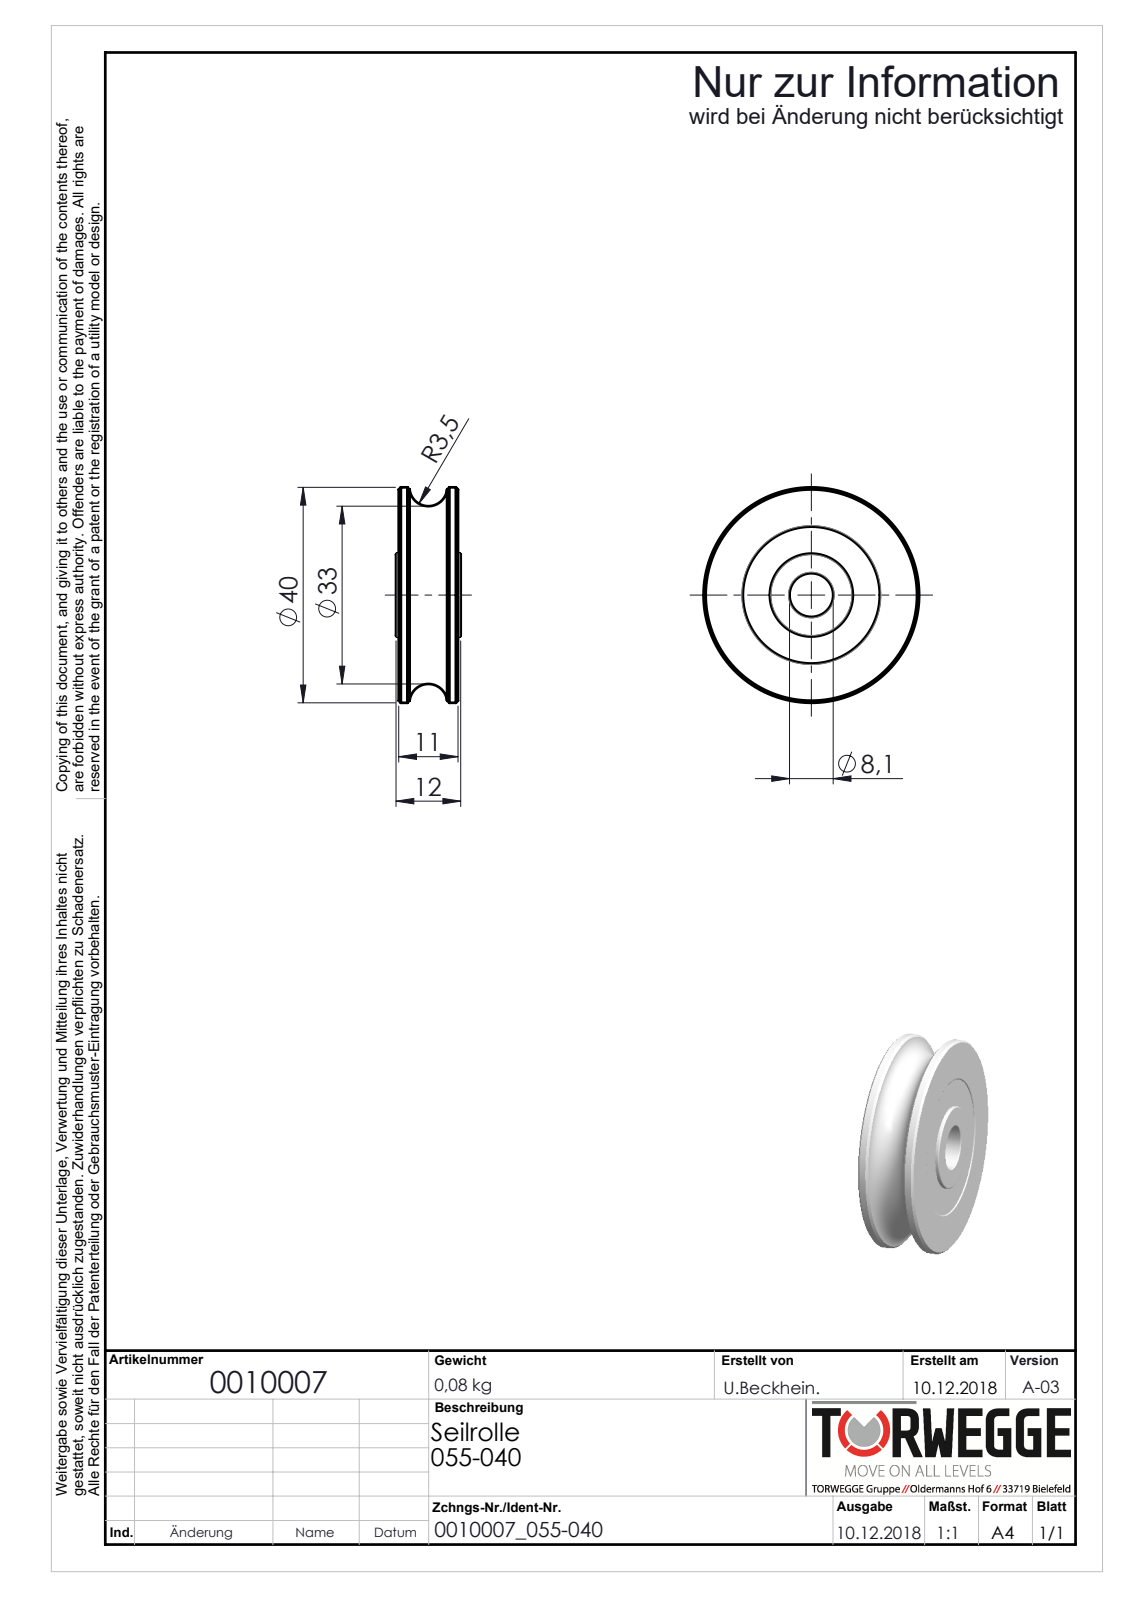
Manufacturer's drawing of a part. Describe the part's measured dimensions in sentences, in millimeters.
The part is named "0010007_055-040_(A-03)". Its 3-D file was written by "SolidWorks 2018 (AUTOMOTIVE_DESIGN)". It is 1 solid with 40 faces: 6 planar, 10 cylindrical and 24 other. Overall it measures 40 by 40 by 12 millimeters. Its volume is 10 981 cubic millimeters and its surface area 4 403 square millimeters. Round holes: 1 of diameter 8.1. Round bosses or shafts: 1 of diameter 40, 1 of diameter 15.4. The main face-to-face distances are 11, 10.8, 10.6, 0.5, 0.7, 11.3, 11.5, 12.
